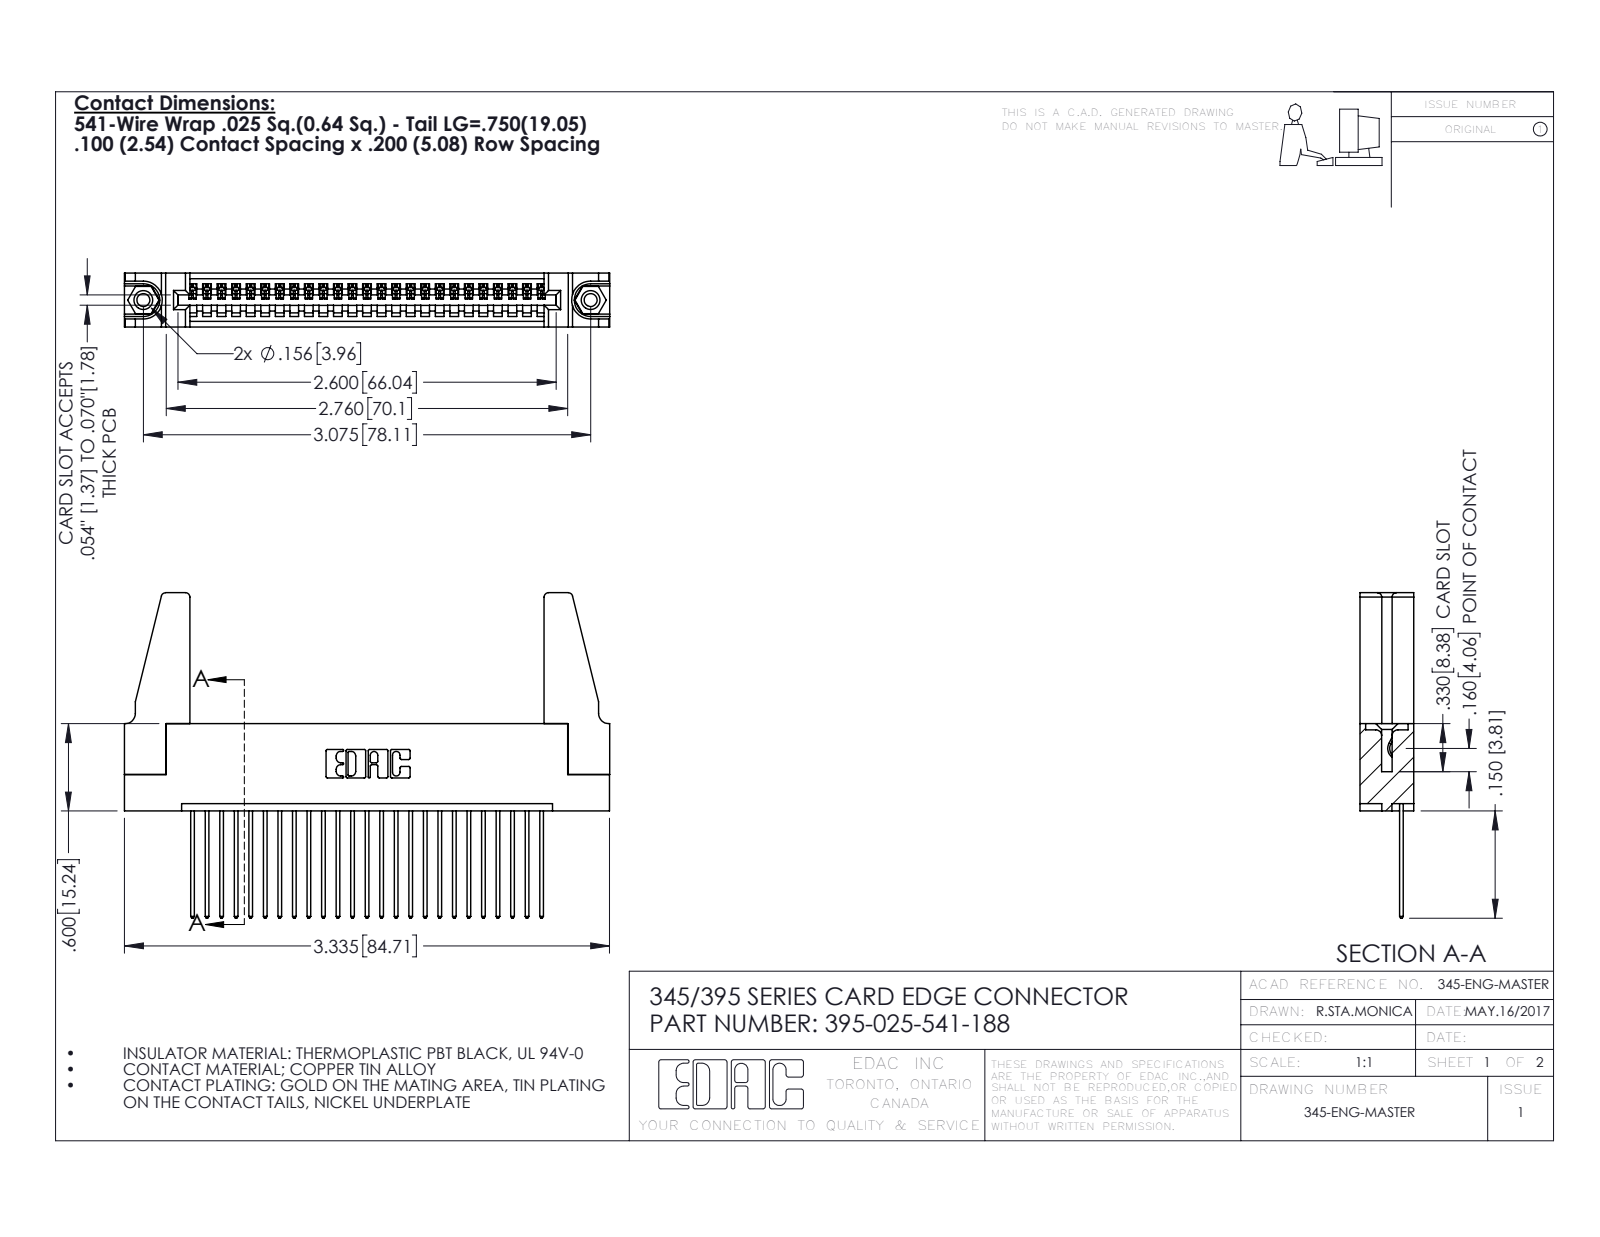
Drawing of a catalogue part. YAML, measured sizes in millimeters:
part_name: "345 Part_Flush Mounting Lugs - 0.156 Dia-TH; 345-220-078_345-220-088; 345-250-001_345-250-001-102; 345-292-001_345-293-141 (+1 more)"
step_written_by: "SolidWorks 2016 (CONFIG_CONTROL_DESIGN)"
units: millimeters
bodies: {solids: 30, faces: 1700, planar: 1152, cylindrical: 532, other: 16}
overall_size: [84.7, 56.8, 9.4]
volume: 11200
surface_area: 14010
round_holes:
  - {diameter: 2.3, count: 2}
  - {diameter: 3.2, count: 2}
  - {diameter: 4, count: 2}
  - {diameter: 1.6, count: 1}
round_bosses_or_shafts:
  - {diameter: 3.9, count: 2}
partial_cylinders:
  - {radius: 0.2, count: 50}
  - {radius: 0.3, count: 50}
  - {radius: 0.3, count: 22}
  - {radius: 0.8, count: 8}
  - {radius: 0.2, count: 6}
  - {radius: 0.8, count: 6}
  - {radius: 0.7, count: 3}
  - {radius: 0.8, count: 2}
face_to_face_distances: [1.8, 7.6, 9.4, 5.1, 2.5, 6.9, 0.6, 5.7, 3.8, 3.8]
hole_center_spacings: [6.9, 72.1, 78.1]
